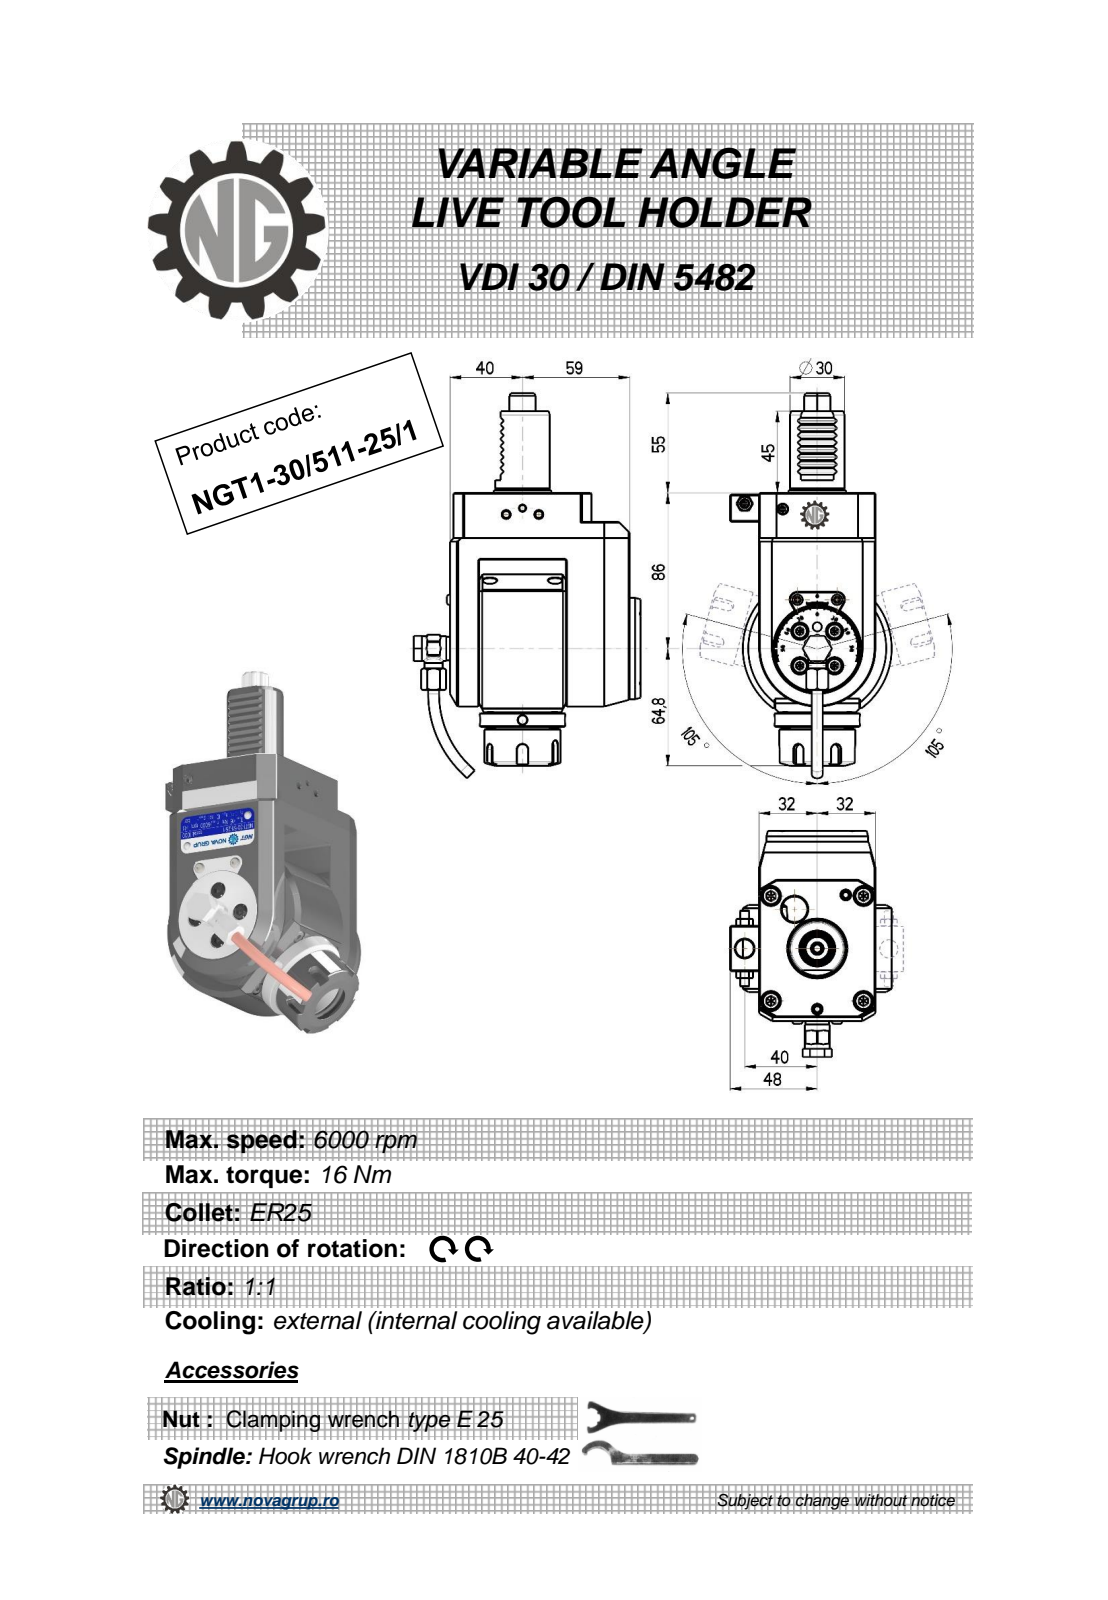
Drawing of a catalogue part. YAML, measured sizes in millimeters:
part_name: "NGT1_30_511_25_1"
step_written_by: "PRO/ENGINEER BY PARAMETRIC TECHNOLOGY CORPORATION, 2010280 (CONFIG_CONTROL_DESIGN)"
units: millimeters
bodies: {solids: 1, faces: 583, planar: 220, cylindrical: 164, other: 199}
overall_size: [212.67, 124.9, 89]
volume: 778938
surface_area: 74557
round_holes:
  - {diameter: 4, count: 3}
  - {diameter: 4.2, count: 2}
  - {diameter: 5, count: 2}
  - {diameter: 10, count: 2}
  - {diameter: 3, count: 1}
  - {diameter: 5.3, count: 1}
  - {diameter: 6.2, count: 1}
  - {diameter: 9, count: 1}
  - {diameter: 9.5, count: 1}
  - {diameter: 11, count: 1}
  - {diameter: 20.3, count: 1}
round_bosses_or_shafts:
  - {diameter: 6, count: 2}
  - {diameter: 5.7, count: 2}
  - {diameter: 82, count: 1}
  - {diameter: 56, count: 1}
  - {diameter: 47, count: 1}
  - {diameter: 42, count: 1}
  - {diameter: 35, count: 1}
  - {diameter: 30, count: 1}
partial_cylinders:
  - {radius: 2.91, count: 16}
  - {radius: 0.26, count: 12}
  - {radius: 0.3, count: 8}
  - {radius: 0.16, count: 6}
  - {radius: 3, count: 5}
  - {radius: 0.5, count: 4}
  - {radius: 1, count: 2}
  - {radius: 5.75, count: 1}
face_to_face_distances: [64, 16, 37, 6, 99, 105, 14, 21, 35, 41]
hole_center_spacings: [0.4, 39.45, 40, 49, 49.4, 63.25, 63.56, 89.44]
